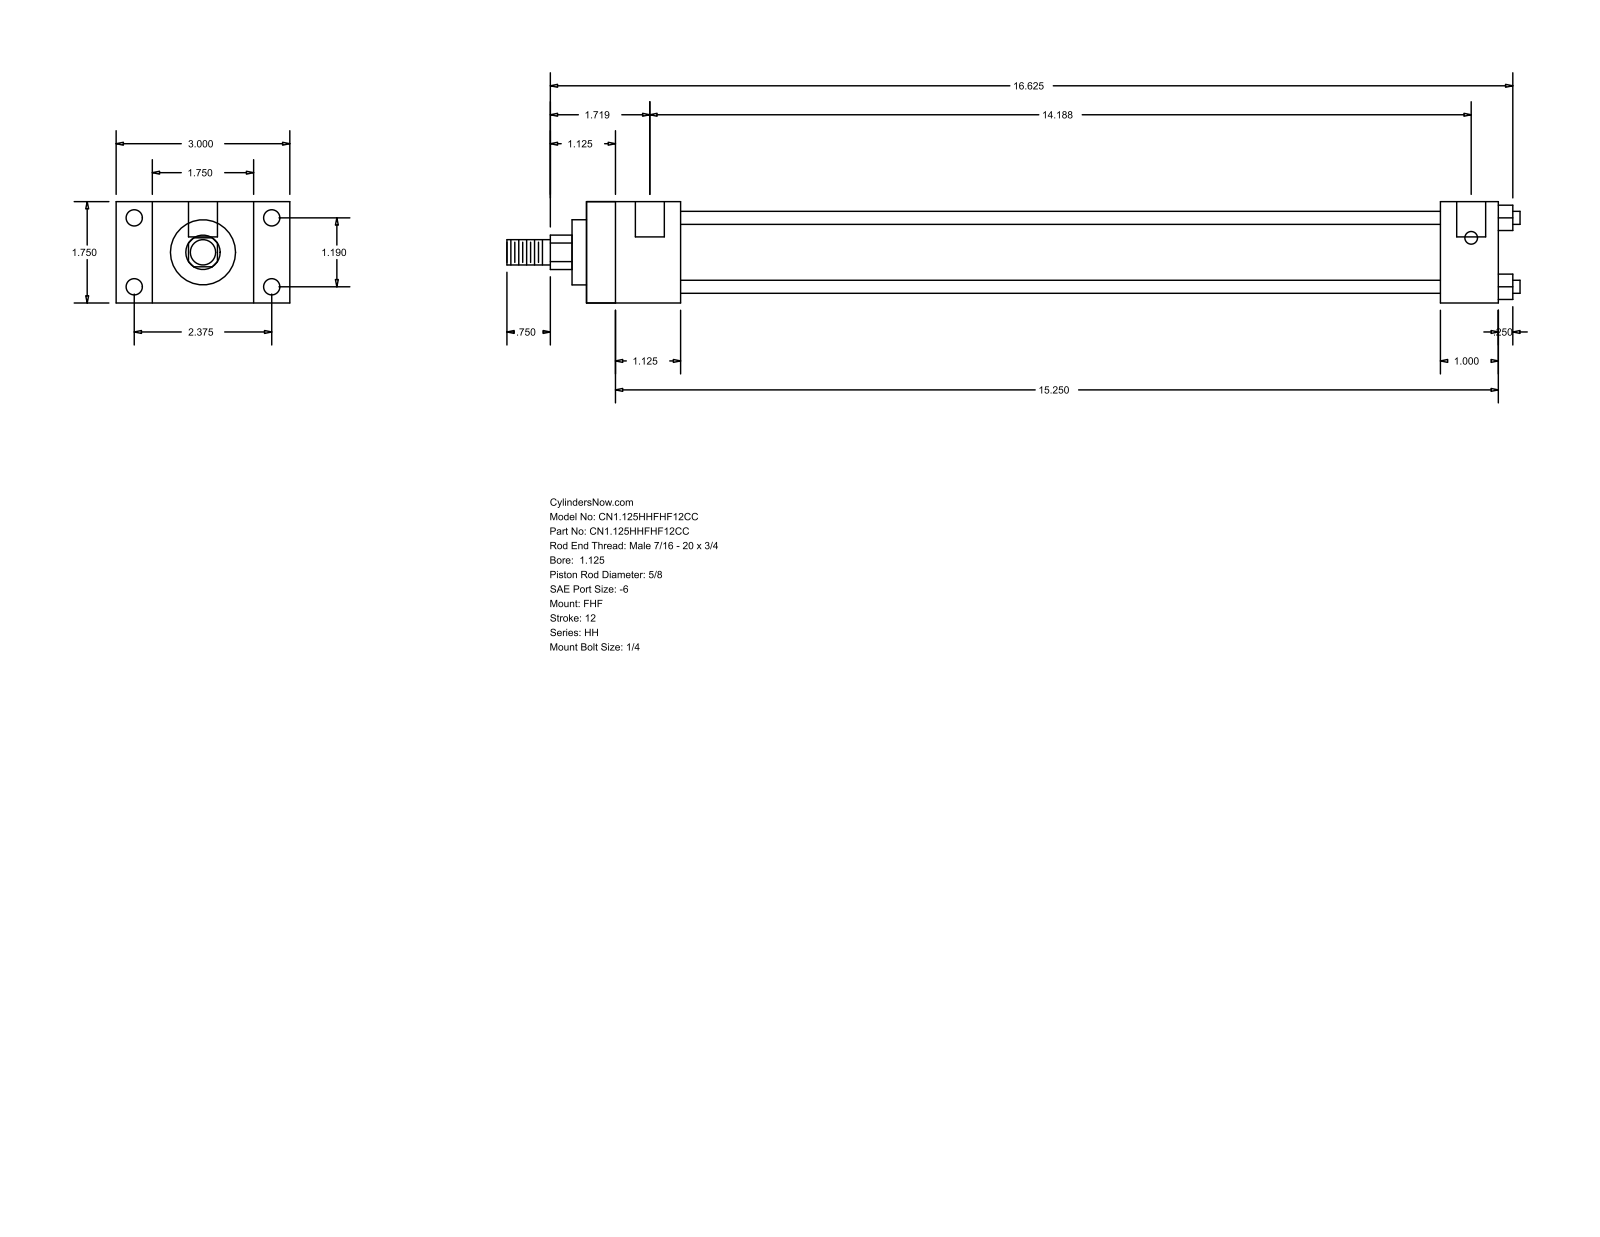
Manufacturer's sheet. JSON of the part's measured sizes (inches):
{"part_name": "HH_FHF__0112_0.625", "step_written_by": "GSSL Pune (CONFIG_CONTROL_DESIGN)", "units": "inches", "bodies": {"solids": 0, "faces": 88, "planar": 60, "cylindrical": 28, "other": 0}, "overall_size": [17.5, 3, 1.75], "round_holes": [[0.219, 4], [0.281, 4], [0.5, 2]], "round_bosses_or_shafts": [[0.225, 4], [1.375, 1], [1.125, 1], [0.625, 1], [0.437, 1]], "partial_cylinders_radius": [[0.297, 1]], "face_to_face_distances": [1.75, 0.625, 2.375, 1.625, 3, 15.75, 14.125, 14.75, 13.125, 1], "hole_center_spacings": [1.19, 2.375, 2.656, 14.063, 0.125, 14.187]}
